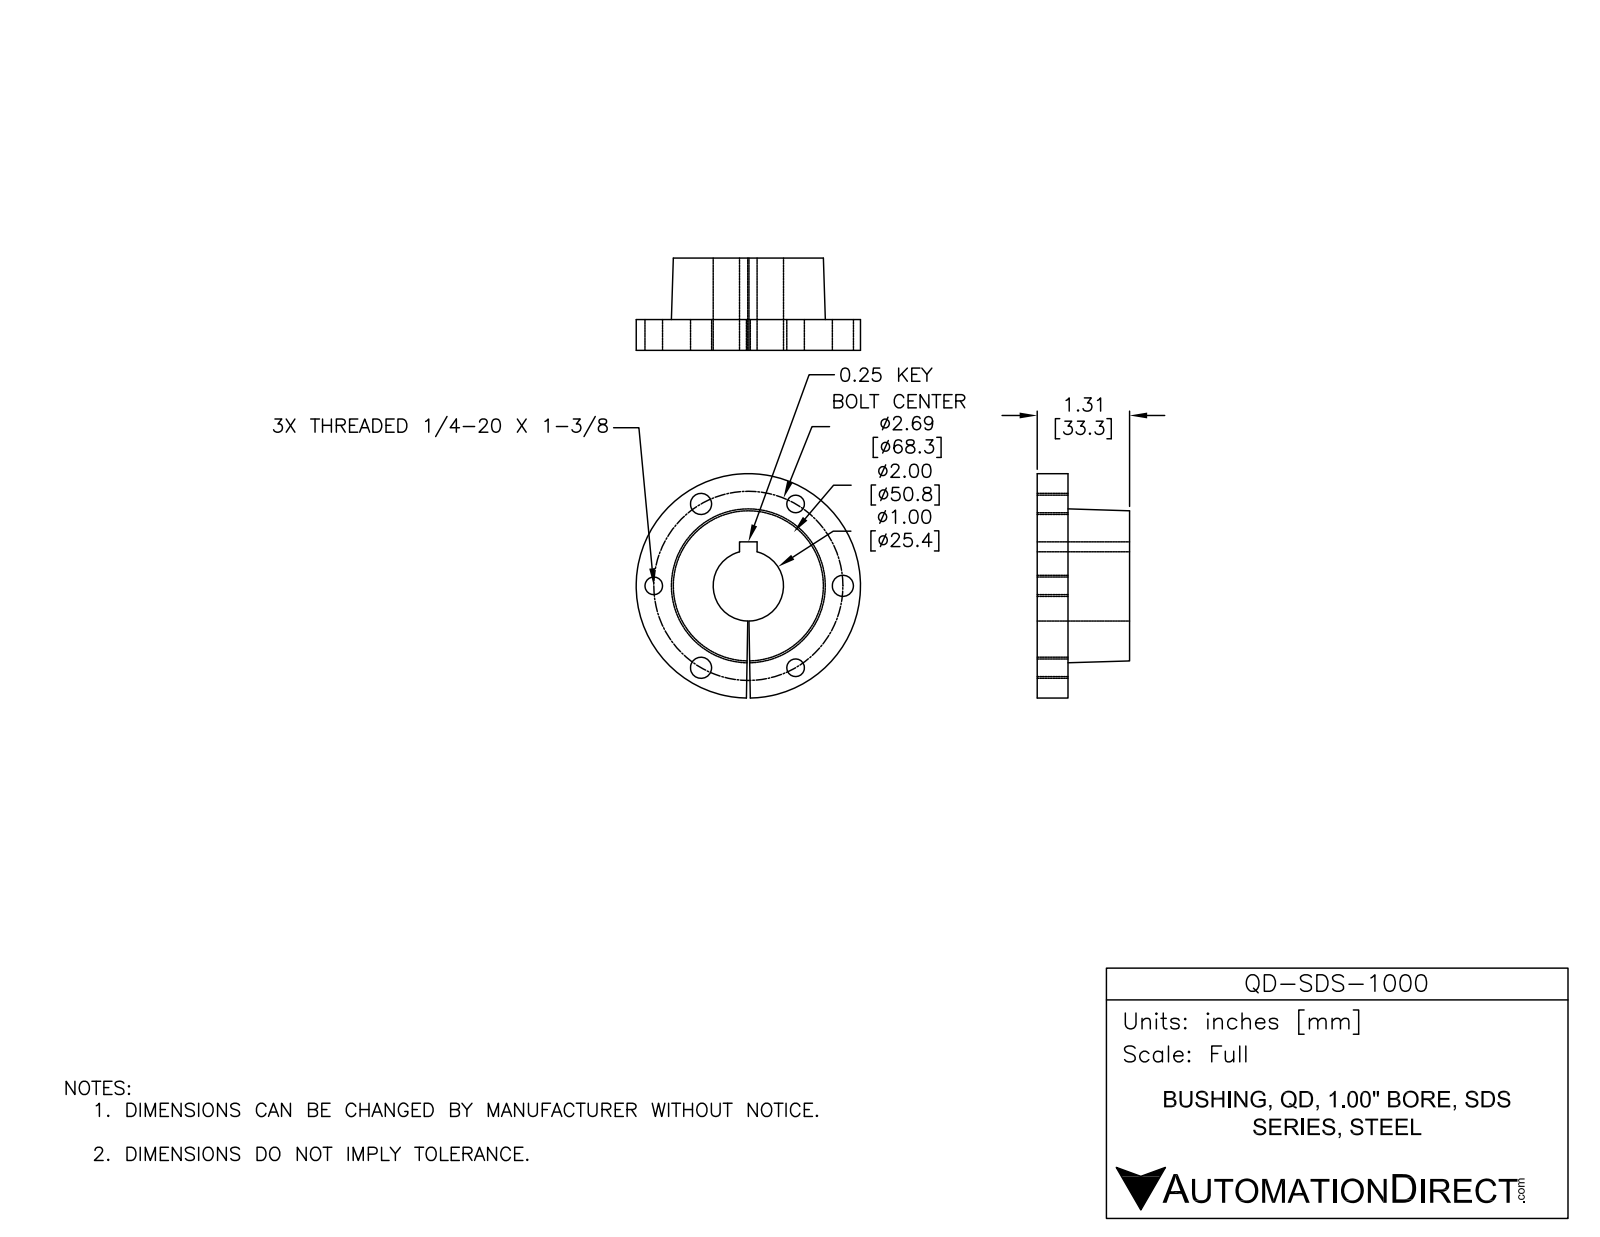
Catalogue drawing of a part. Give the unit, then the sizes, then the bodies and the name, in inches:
Units: inches
Overall size (bounding box): 3.188 × 3.187 × 1.313
Round holes (diameter × count): ⌀0.25 ×3, ⌀0.3 ×3, ⌀1 ×1
Round bosses / shafts (diameter × count): ⌀3.187 ×1
Main face-to-face distances: 0.437, 1.313, 0.875, 0.25
Hole centre spacings: 1.344, 2.328, 1.344, 2.688, 2.687
Volume: 5.436 in³ · Surface area: 32.31 in²
Bodies: 1 solid, 29 faces (8 planar, 18 cylindrical, 3 other)
Part name (STEP PRODUCT): QD-SDS-1000
STEP written by: SolidWorks 2014 (AUTOMOTIVE_DESIGN)
